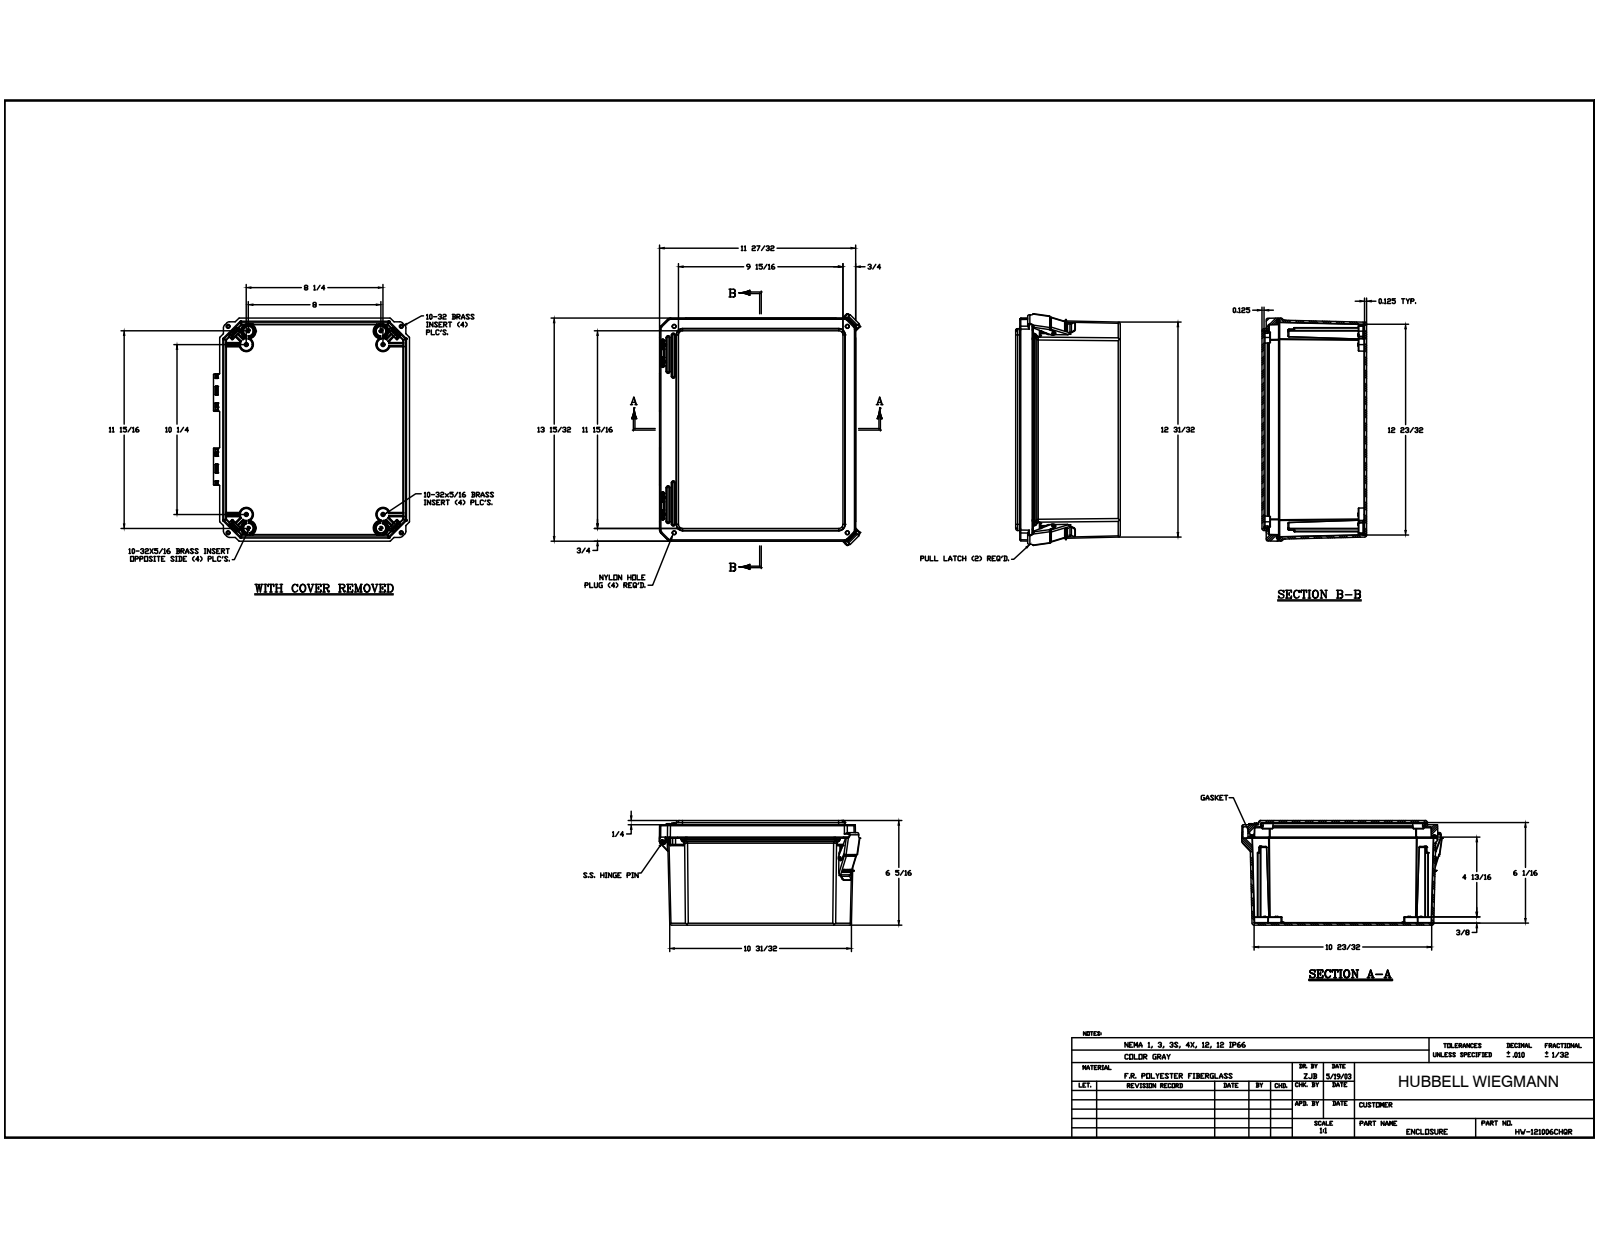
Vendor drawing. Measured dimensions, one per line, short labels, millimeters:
name: DS121006BOX; BRASS INSERT-(; BRASS INSERT-(_1; BRASS INSERT-(_2 (+6 more)
written by: Autodesk Inventor 2014 (AUTOMOTIVE_DESIGN)
unit: mm
bodies: 35 solids, 2443 faces (823 planar, 988 cylindrical, 632 other)
size: 358.6 × 309 × 160.28
volume: 1 542 000 mm³; area: 840 381 mm²
holes: 16× ⌀3.96, 8× ⌀3.86, 6× ⌀3.43, 4× ⌀3.81, 4× ⌀6.4, 4× ⌀6.43, 2× ⌀3.43, 2× ⌀5.56, 2× ⌀5.77, 2× ⌀7.94, 2× ⌀9.52, 1× ⌀3.48
bosses: 16× ⌀6.25, 4× ⌀22.1, 4× ⌀5.3, 2× ⌀11.05, 2× ⌀7.62, 1× ⌀3.43
rounds: 203× R0.25, 84× R0.51, 80× R0.13, 65× R0.76, 33× R1.52, 26× R1.59, 26× R2.29, 24× R0.76
face distances: 3.17, 157.11, 160.28, 153.94, 3.53, 3.55, 3.56, 6.35, 150.76, 3.18
hole spacings: 20.92, 271.58, 281.04, 289.7, 289.72, 348.66, 260.34, 6.35
